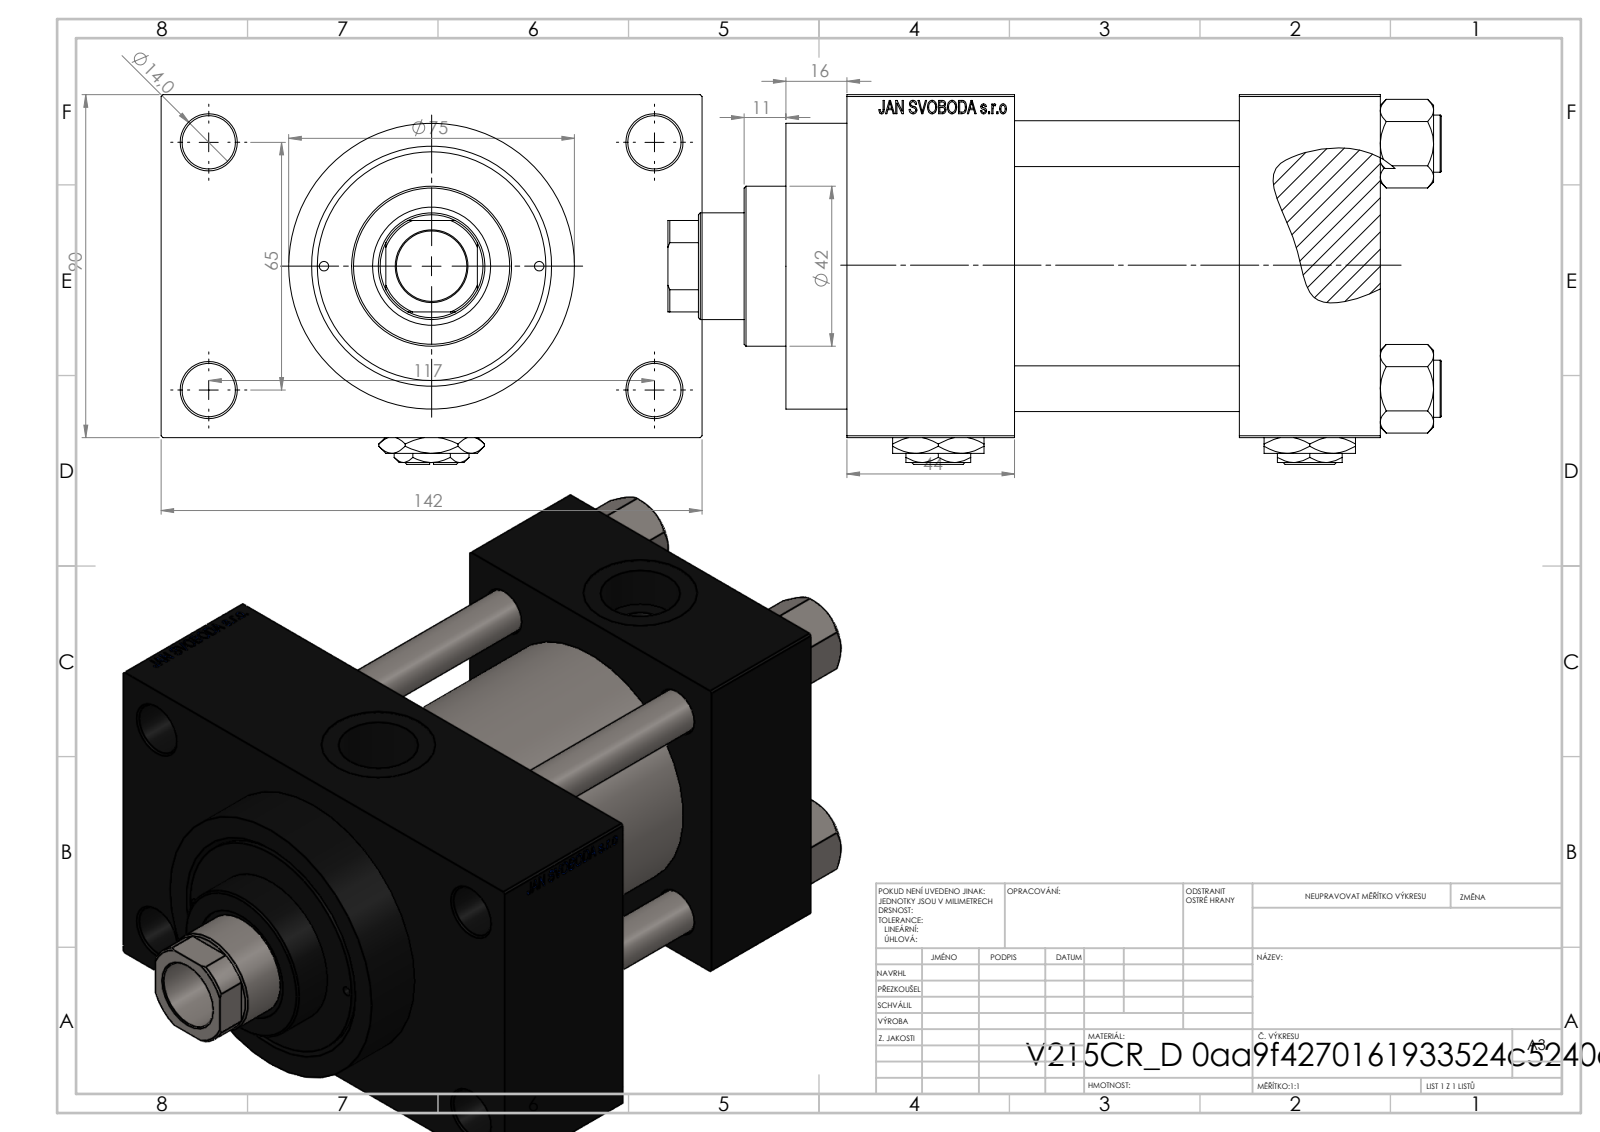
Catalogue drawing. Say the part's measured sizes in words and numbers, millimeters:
The part is named "V215_VC_A; V215CR_D_TYCINKA; V215CR_D_Body; NUT_M5_D (+2 more)". Its 3-D file was written by "SolidWorks 2019 (CONFIG_CONTROL_DESIGN)". It is 13 solids with 1213 faces: 547 planar, 104 cylindrical and 562 other. Overall it measures 203 by 142 by 97 millimeters. Its volume is 1 099 000 cubic millimeters and its surface area 203 152 square millimeters. Round holes: 4 of diameter 12, 4 of diameter 14, 2 of diameter 2.5, 2 of diameter 7, 2 of diameter 20.96, 2 of diameter 30, 1 of diameter 18.5, 1 of diameter 28, 1 of diameter 31, 1 of diameter 50, 1 of diameter 60, 1 of diameter 63. Round bosses or shafts: 4 of diameter 15, 1 of diameter 75, 1 of diameter 69, 1 of diameter 42. Partial cylindrical surfaces (rounded edges, fillets, slot ends): 1 of radius 13.5. The main face-to-face distances are 90, 59, 37, 96, 140, 103, 44, 26, 116, 142. The hole center spacings are 26.35, 32.39, 44.4, 45.47, 64.3, 66.92, 68.42, 69.81.
